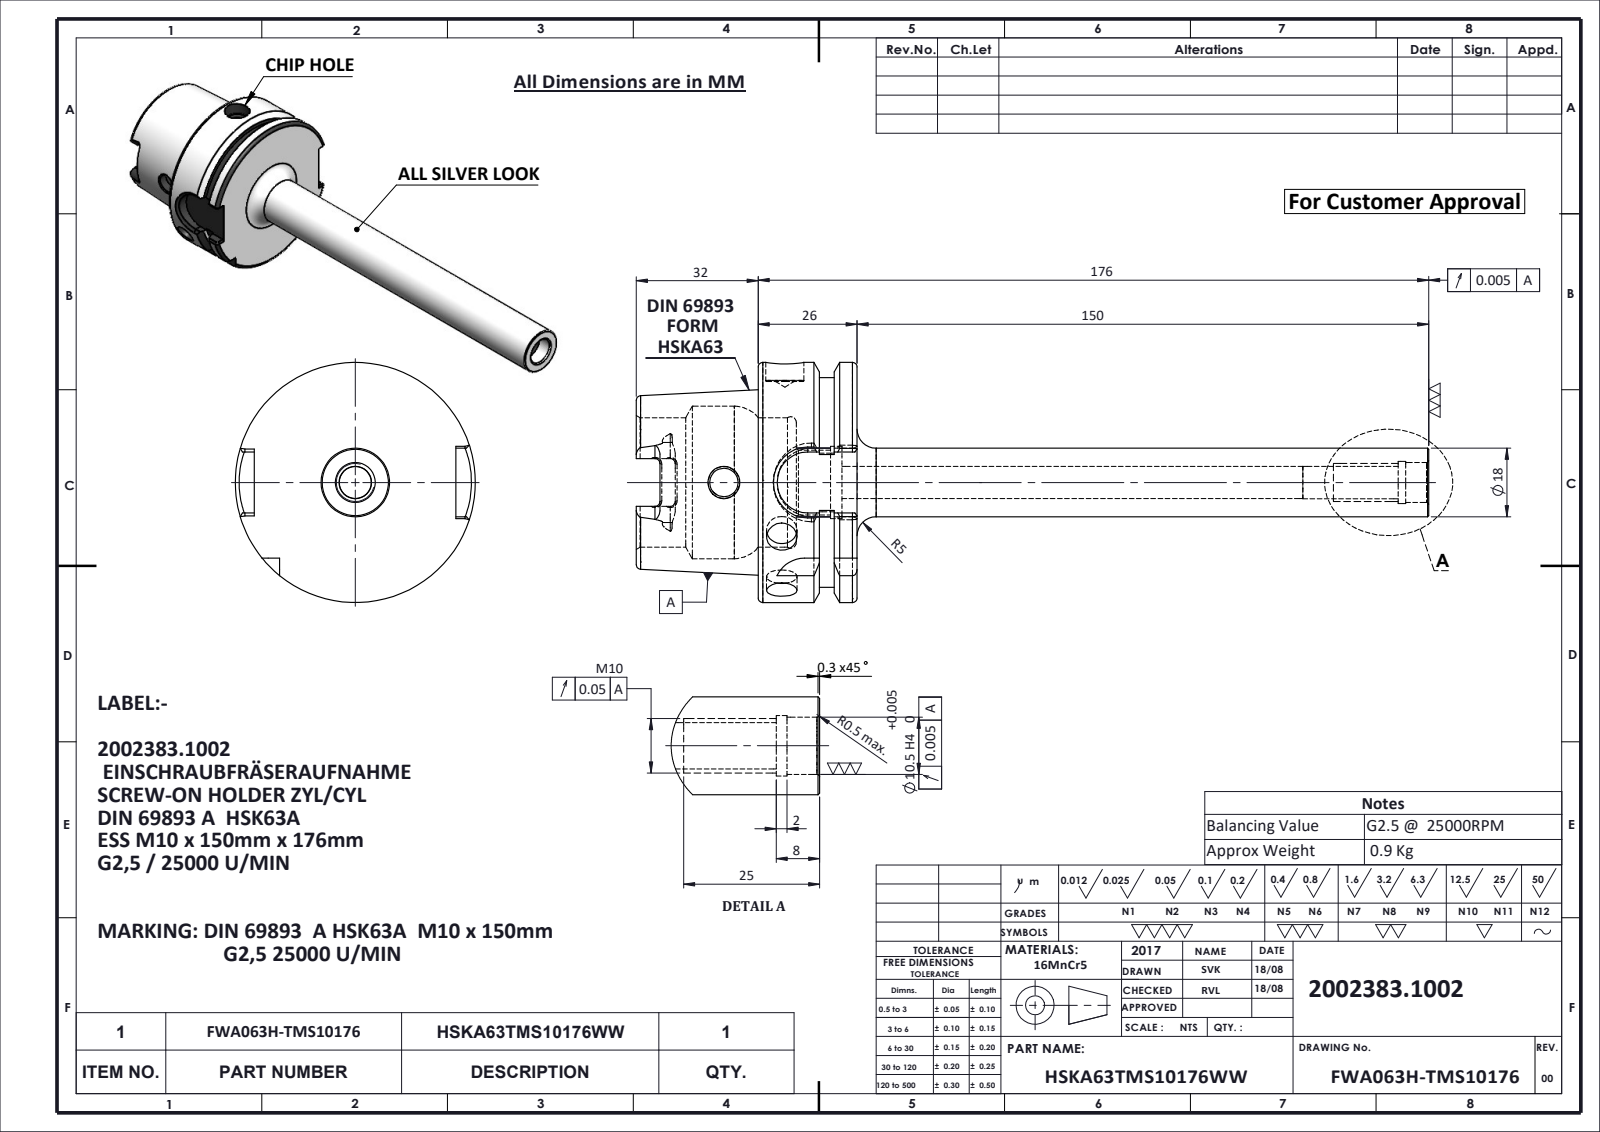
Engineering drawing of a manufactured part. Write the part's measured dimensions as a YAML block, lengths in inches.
part_name: "FWA063H-TMS10176; HSKA63TMS10176WW"
step_written_by: "SolidWorks 2024 (CONFIG_CONTROL_DESIGN)"
units: inches
bodies: {solids: 1, faces: 168, planar: 51, cylindrical: 53, other: 64}
overall_size: [8.189, 2.48, 2.48]
volume: 6.756
surface_area: 53.85
round_holes:
  - {diameter: 0.315, count: 2}
  - {diameter: 0.295, count: 1}
  - {diameter: 0.331, count: 1}
  - {diameter: 0.335, count: 1}
  - {diameter: 0.394, count: 1}
  - {diameter: 0.413, count: 1}
  - {diameter: 0.437, count: 1}
  - {diameter: 0.669, count: 1}
  - {diameter: 0.748, count: 1}
  - {diameter: 1.339, count: 1}
  - {diameter: 1.575, count: 1}
round_bosses_or_shafts:
  - {diameter: 2.48, count: 1}
  - {diameter: 2.165, count: 1}
  - {diameter: 0.709, count: 1}
partial_cylinders:
  - {radius: 0.051, count: 6}
  - {radius: 0.113, count: 4}
  - {radius: 0.315, count: 2}
  - {radius: 0.354, count: 1}
face_to_face_distances: [1.022, 0.394, 0.628, 1.26, 1.654, 2.281, 2.083, 2.126, 0.866, 0.472]
